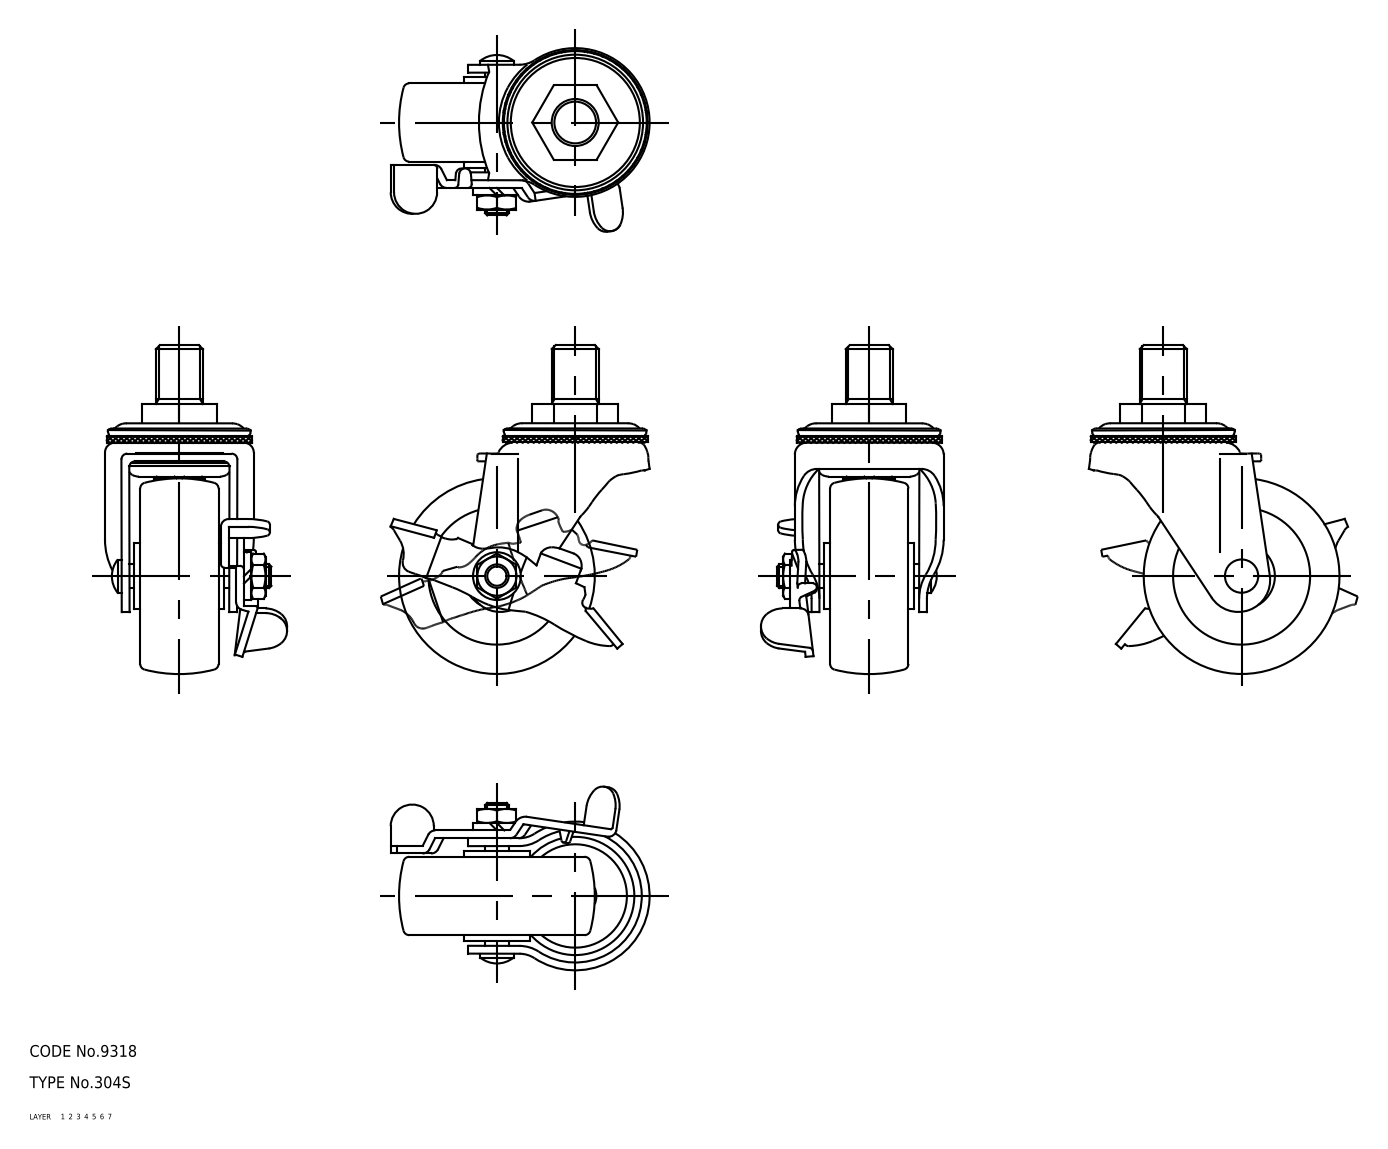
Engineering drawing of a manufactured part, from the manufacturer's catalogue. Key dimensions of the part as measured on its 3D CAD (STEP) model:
Part name (STEP PRODUCT): lever; wheel; main shaft; axle (+1 more)
STEP written by: CADfix (AUTOMOTIVE_DESIGN)
Units: millimetres
Bodies: 5 solids, 273 faces (0 planar, 0 cylindrical, 273 other)
Overall size (bounding box): 84 × 66.19 × 46.81
Volume: 58 638 mm³ · Surface area: 22 097 mm²
